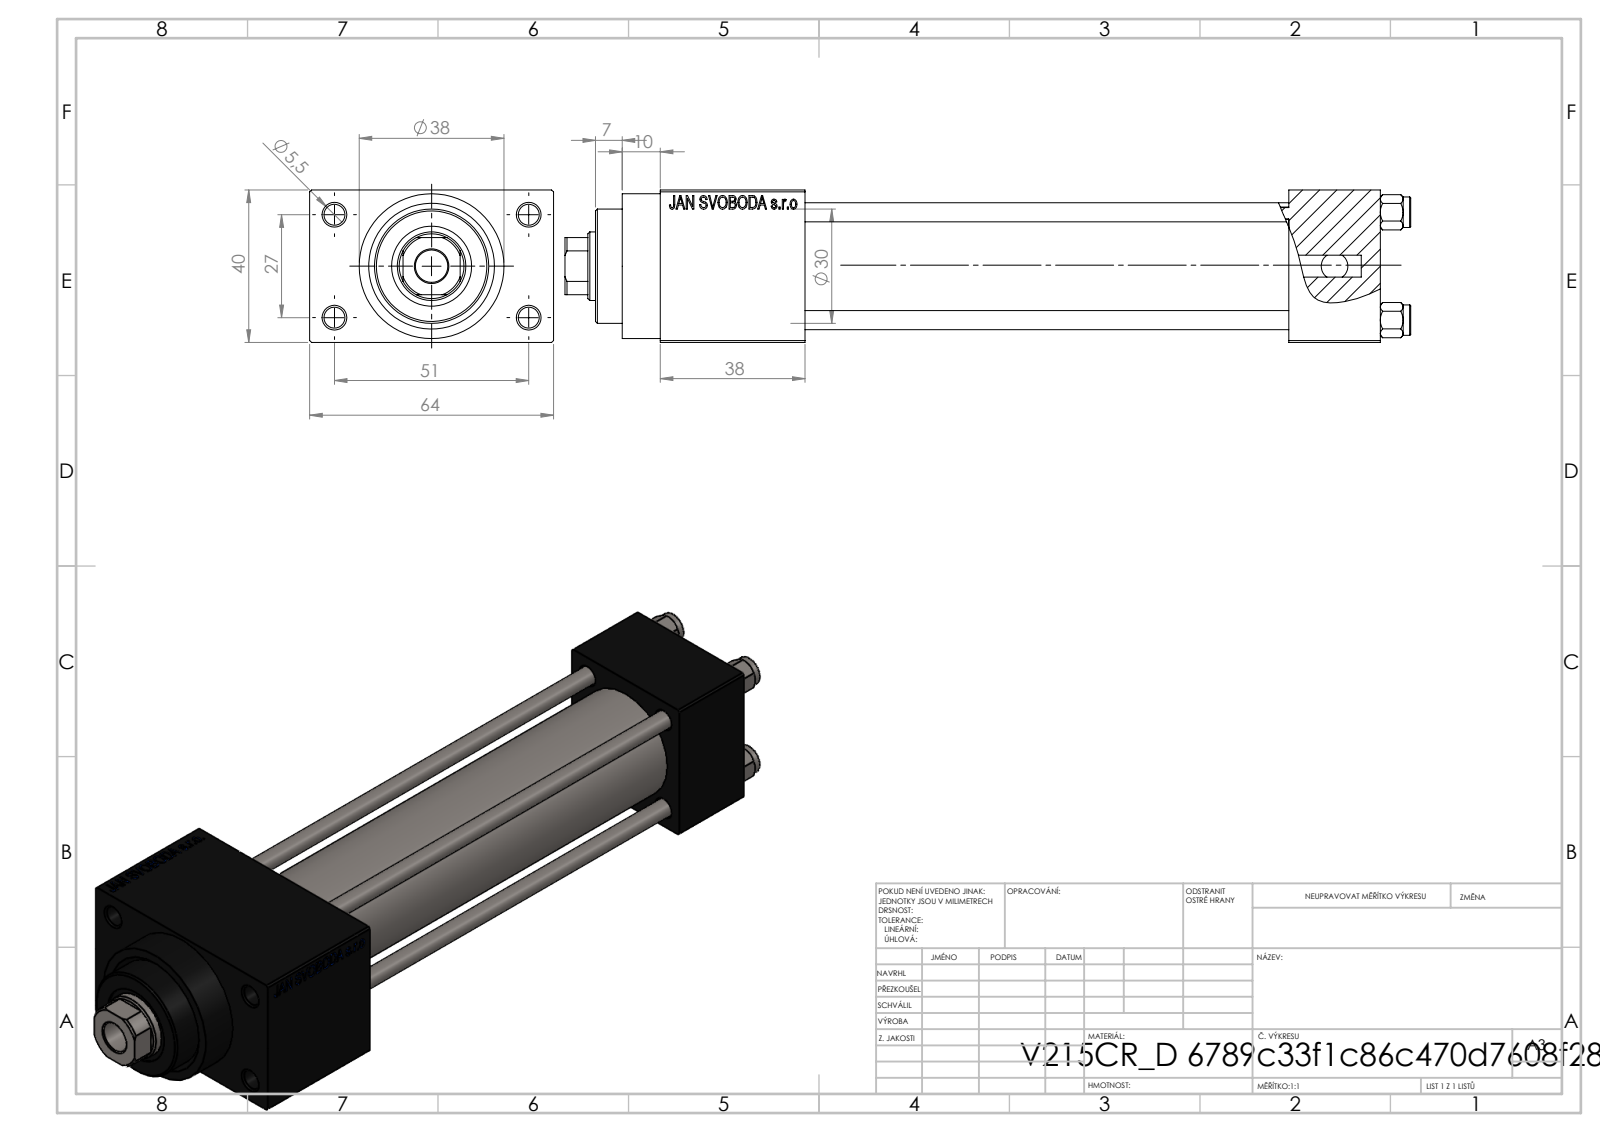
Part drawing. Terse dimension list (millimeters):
name: V215CR_D_TYCINKA; V215CR_VCP_D; V215CR_D_Body; NUT_M5_D (+1 more)
written by: SolidWorks 2019 (CONFIG_CONTROL_DESIGN)
unit: mm
bodies: 11 solids, 1101 faces (495 planar, 86 cylindrical, 520 other)
size: 222 × 64 × 40
volume: 226 874 mm³; area: 88 254 mm²
holes: 4× ⌀5, 4× ⌀5.5, 3× ⌀20, 2× ⌀7, 2× ⌀13.16, 1× ⌀8.5, 1× ⌀18, 1× ⌀21, 1× ⌀25, 1× ⌀30
bosses: 4× ⌀8, 1× ⌀38, 1× ⌀31
rounds: 1× R8.5
face distances: 40, 12, 127, 24, 151, 52, 38, 189, 165, 64
hole spacings: 11.37, 20.01, 28.3, 28.85, 29.89, 39.66, 48.34, 27
